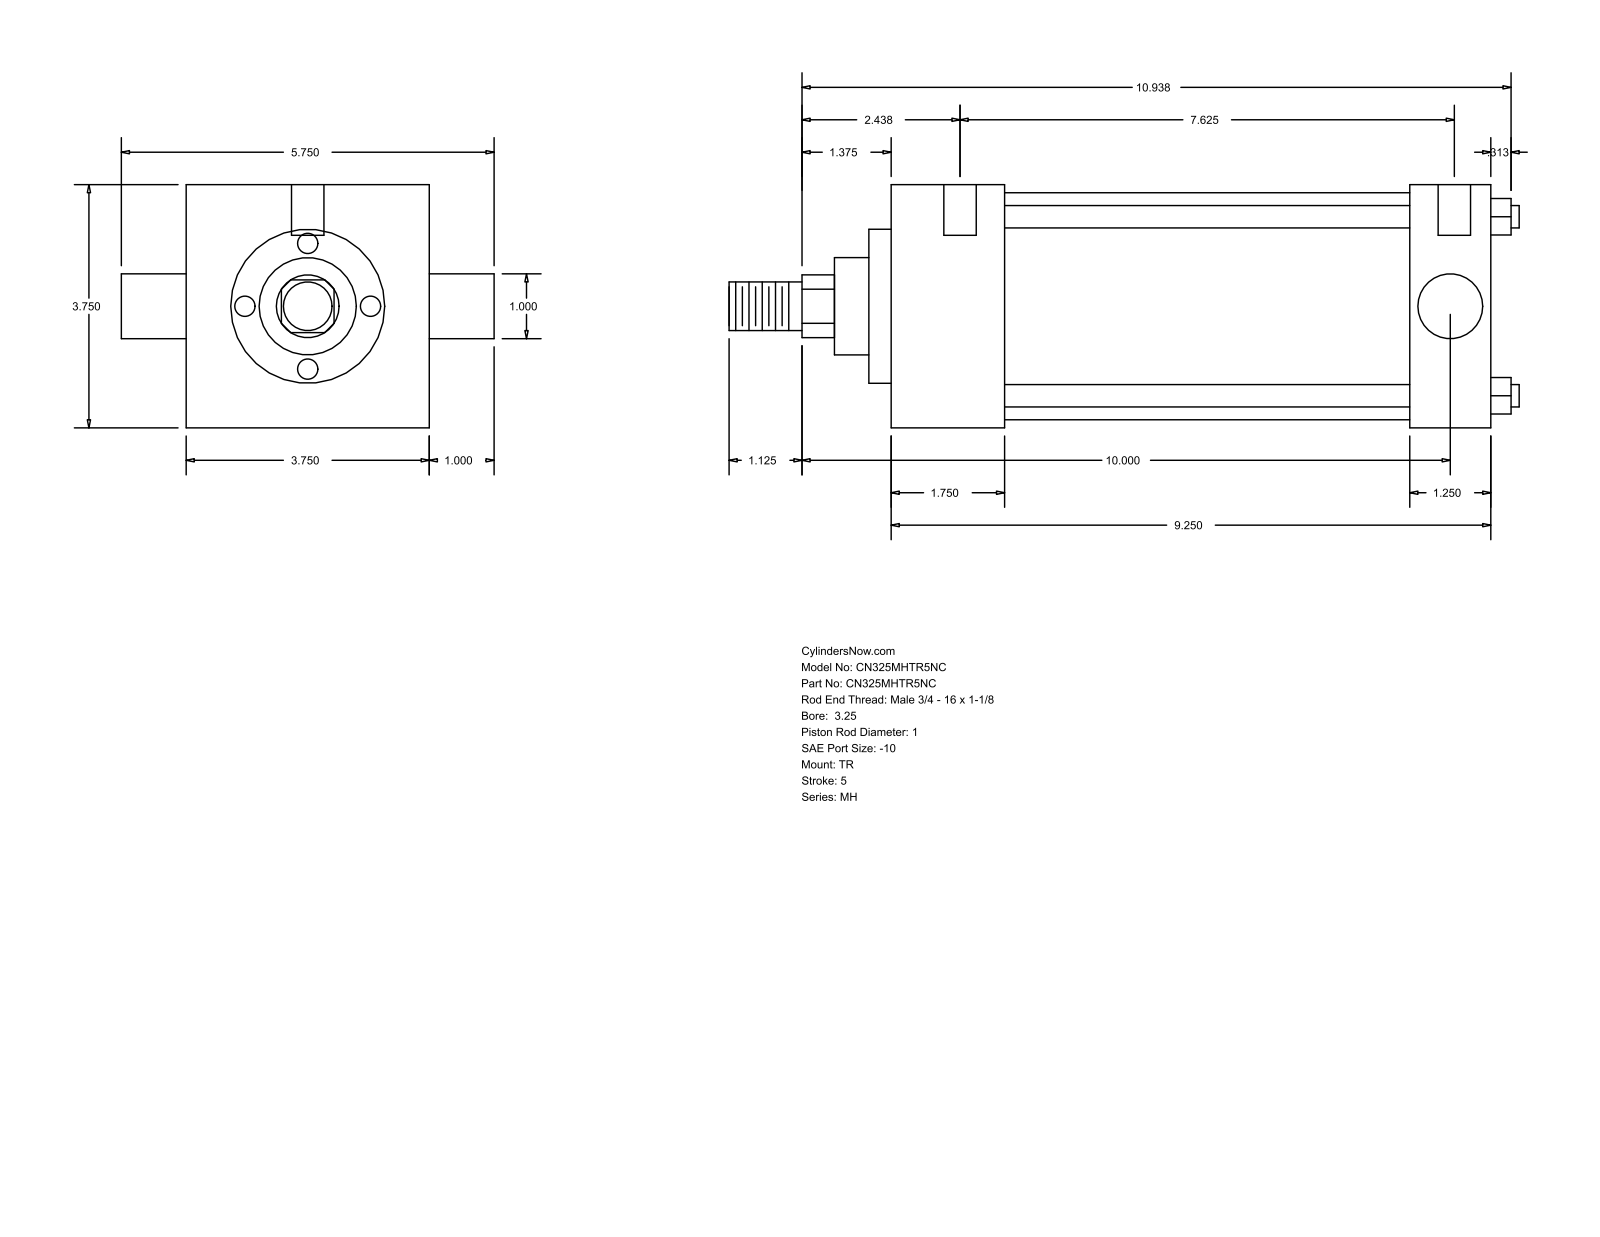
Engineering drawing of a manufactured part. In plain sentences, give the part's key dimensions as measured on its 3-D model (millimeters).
The part is named "MH_TR__0325_1". Its 3-D file was written by "GSSL Pune (CONFIG_CONTROL_DESIGN)". It is 0 solids with 86 faces: 61 planar, 25 cylindrical and 0 other. Overall it measures 309.56 by 146.05 by 95.25 millimeters. Round holes: 3 of diameter 5.56, 2 of diameter 12.7. Round bosses or shafts: 4 of diameter 8.76, 2 of diameter 25.4, 1 of diameter 88.9, 1 of diameter 60.33, 1 of diameter 38.1, 1 of diameter 19.05. Partial cylindrical surfaces (rounded edges, fillets, slot ends): 1 of radius 12.29. The main face-to-face distances are 95.24, 234.96, 44.46, 203.2, 158.74, 190.5, 31.76, 8.73, 53.19, 211.93. The hole center spacings are 1.58, 4.76, 193.68, 195.26, 198.44, 200.02.
